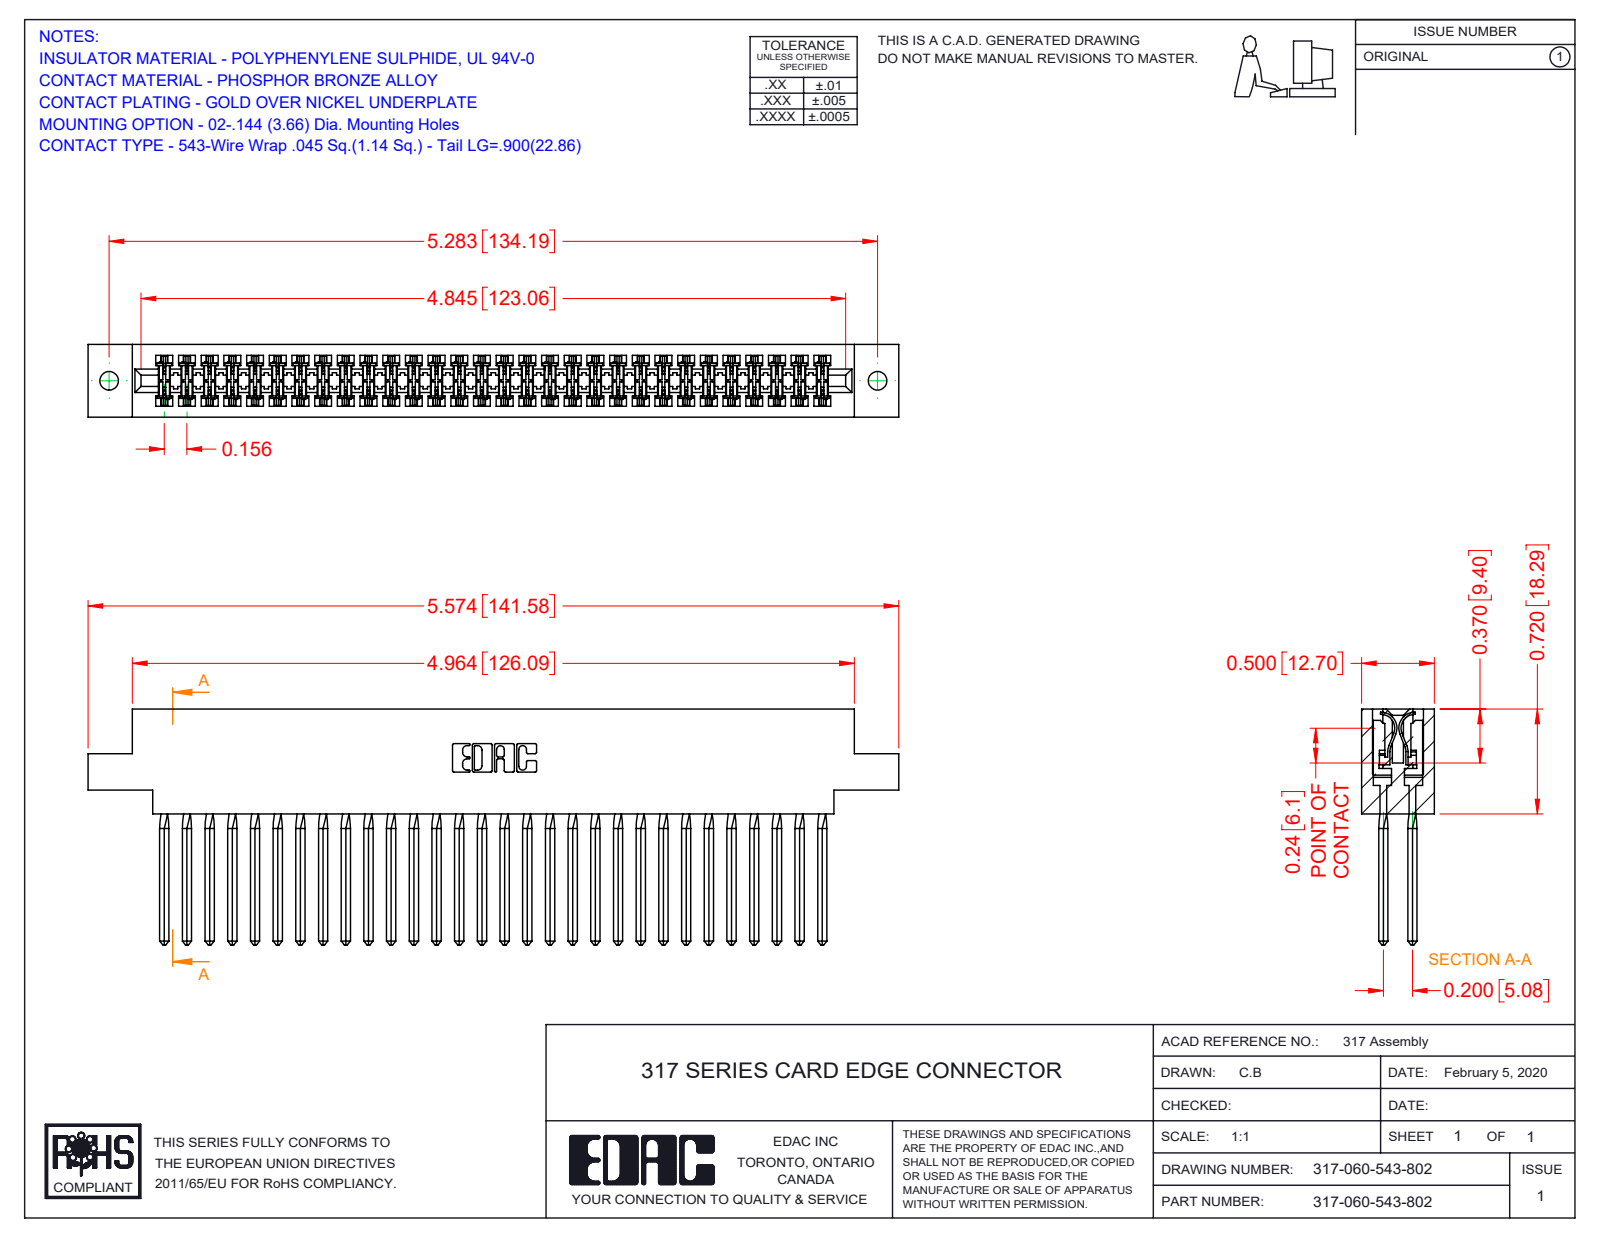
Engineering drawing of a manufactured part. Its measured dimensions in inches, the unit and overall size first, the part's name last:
Units: inches
Overall size (bounding box): 5.574 × 1.62 × 0.5
Round holes (diameter × count): ⌀0.128 ×2
Partial cylindrical surfaces — rounded edges, fillets, slot ends (radius × count): R0.015 ×120, R0.01 ×22, R0.007 ×6, R0.031 ×6, R0.026 ×3, R0.095 ×2, R0.1 ×2, R0.11 ×2
Main face-to-face distances: 0.5, 0.075, 0.425, 0.35, 0.11, 0.195, 0.094, 0.2, 0.72, 0.115
Hole centre spacings: 5.283
Volume: 1.441 in³ · Surface area: 54.4 in²
Bodies: 61 solids, 5442 faces (4438 planar, 764 cylindrical, 240 other)
Part name (STEP PRODUCT): 317-290-001_543; 317-060-543-802; 317 Part_.144 Dia
STEP written by: SolidWorks 2016 (CONFIG_CONTROL_DESIGN)
